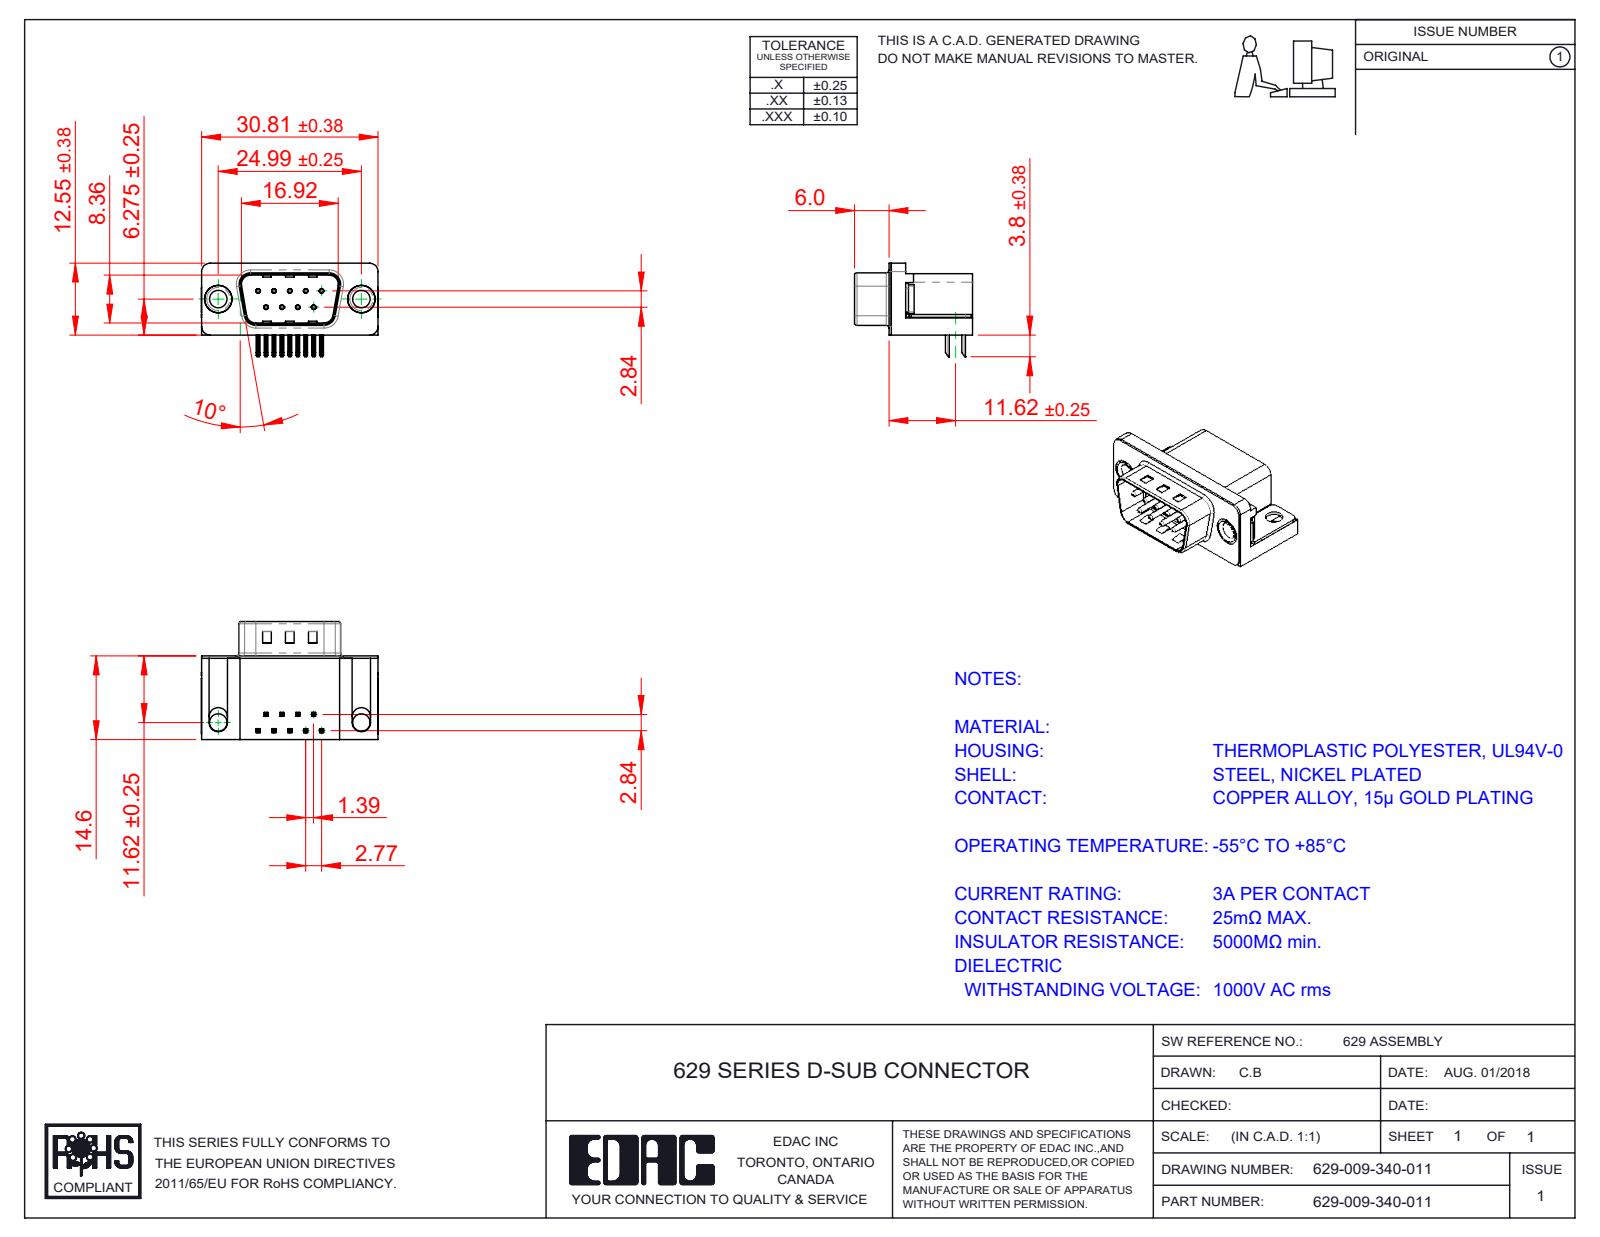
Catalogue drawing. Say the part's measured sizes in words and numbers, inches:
The part is named "629 Contact Top; 629 Housing_09 Socket; 629 Shell_09 Socket; 629 Contact Bottom (+3 more)". Its 3-D file was written by "SolidWorks 2020 (CONFIG_CONTROL_DESIGN)". It is 15 solids with 949 faces: 571 planar, 297 cylindrical and 81 other. Overall it measures 1.216 by 0.811 by 0.644 inches. Its volume is 0.226 cubic inches and its surface area 7.29 square inches. Round holes: 9 of diameter 0.014, 9 of diameter 0.031, 4 of diameter 0.12, 2 of diameter 0.157, 2 of diameter 0.189, 2 of diameter 0.197. Round bosses or shafts: 9 of diameter 0.03, 2 of diameter 0.193, 2 of diameter 0.187, 2 of diameter 0.152. Partial cylindrical surfaces (rounded edges, fillets, slot ends): 44 of radius 0.01, 18 of radius 0.005, 16 of radius 0.039, 9 of radius 0.02, 8 of radius 0.059, 8 of radius 0.063, 4 of radius 0.035, 4 of radius 0.079. The main face-to-face distances are 0.016, 0.559, 0.407, 0.575, 0.02, 0.114, 0.461, 0.098, 0.083, 0.264. The hole center spacings are 0.124, 0.109, 0.218, 0.198, 0.198, 0.327, 0.294, 0.295.
